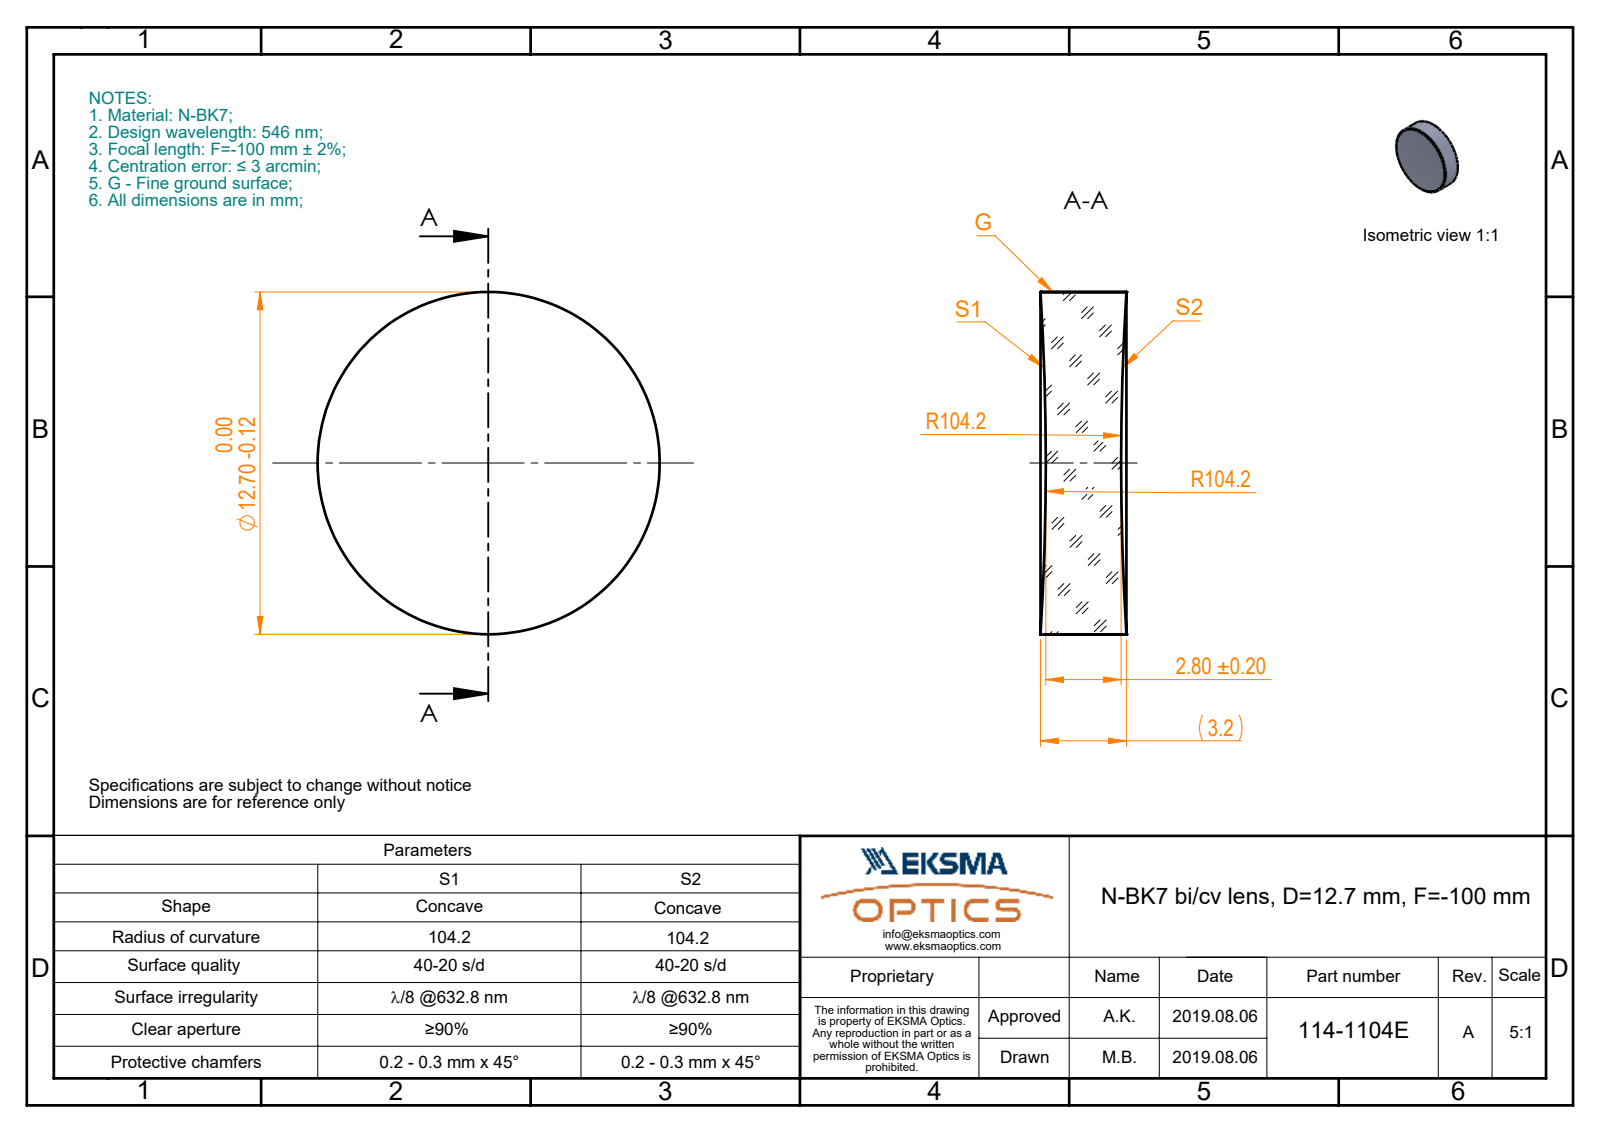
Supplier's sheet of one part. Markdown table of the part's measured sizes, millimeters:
| quantity | value |
| --- | --- |
| part name | 114-0118E BK7 bi-cv 12.7 F-100 |
| STEP written by | SolidWorks 2017 (CONFIG_CONTROL_DESIGN) |
| units | millimeters |
| bodies | 1 solid, 6 faces (0 planar, 2 cylindrical, 4 other) |
| overall size | 12.7 × 12.7 × 3.19 |
| volume | 379 mm³ |
| surface area | 381 mm² |
| round bosses / shafts (diameter × count) | 12.7 × 1 |
